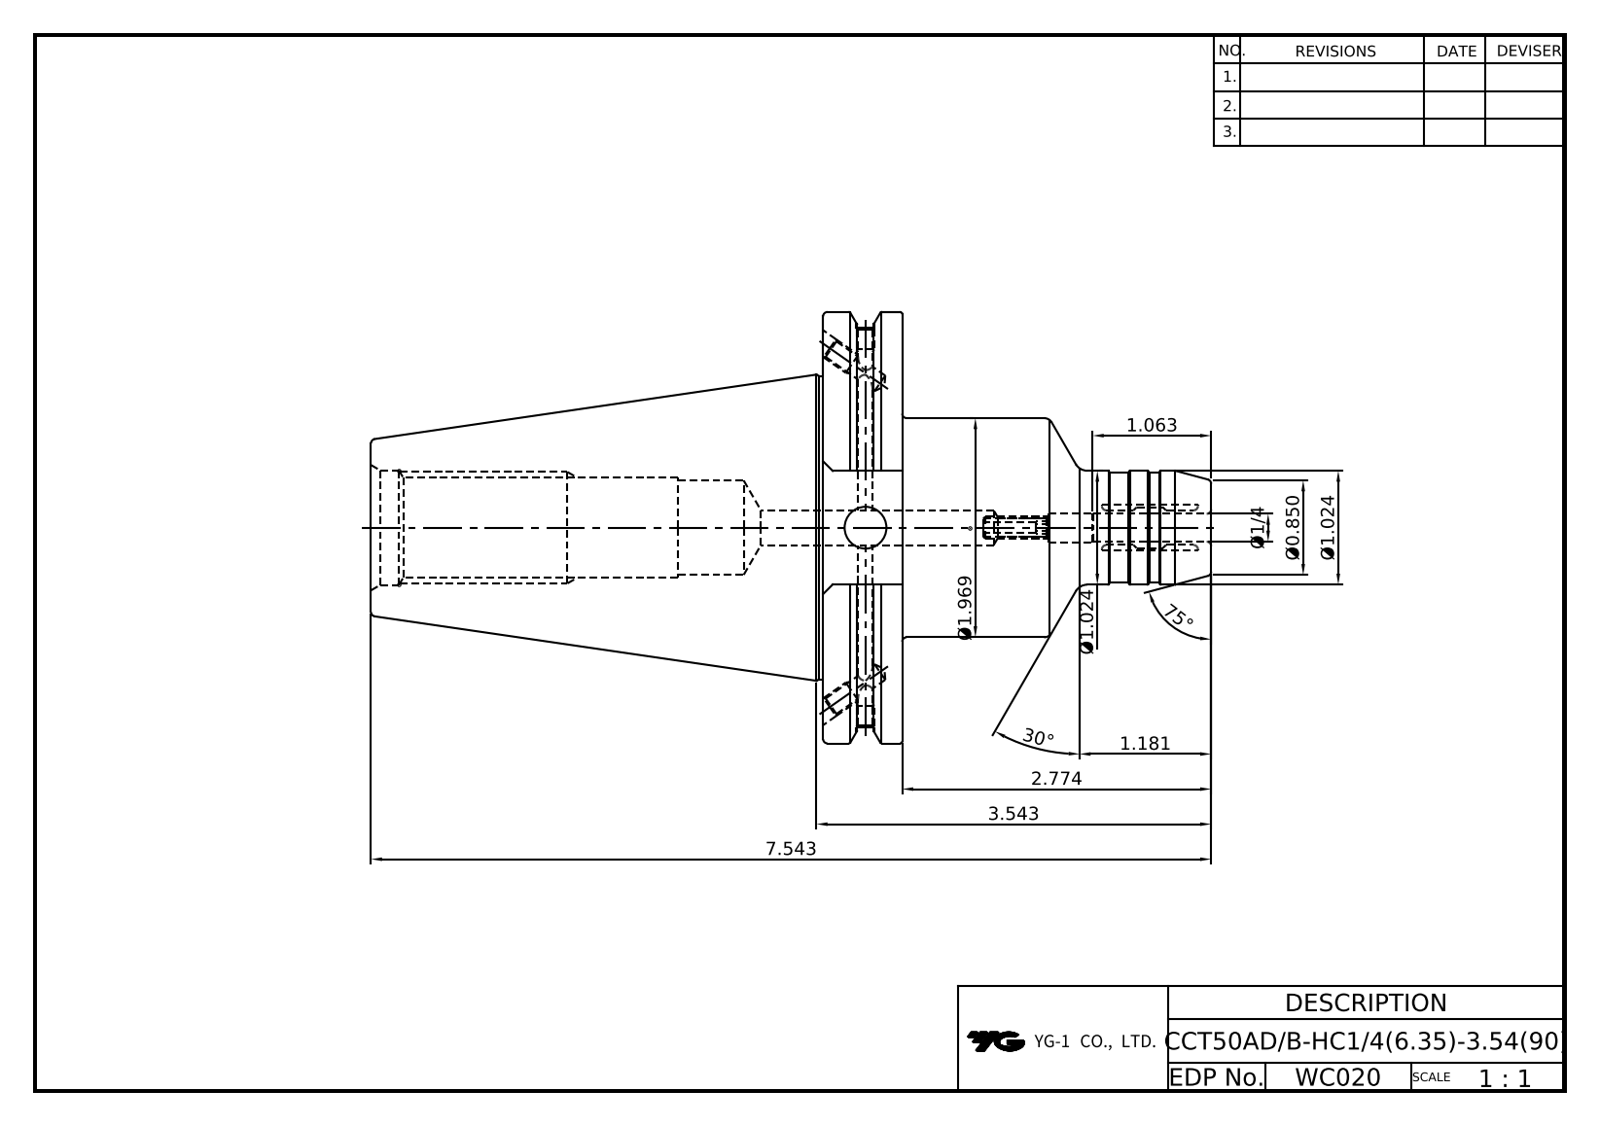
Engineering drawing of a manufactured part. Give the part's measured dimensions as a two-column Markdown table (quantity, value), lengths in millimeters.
| quantity | value |
| --- | --- |
| part name | CCT50ADB-HC6.35-90 |
| STEP written by | Autodesk Inventor 2022 (AUTOMOTIVE_DESIGN) |
| units | millimeters |
| bodies | 1 solid, 110 faces (38 planar, 33 cylindrical, 39 other) |
| overall size | 191.6 × 98.42 × 94.69 |
| volume | 421 825 mm³ |
| surface area | 53 408 mm² |
| round holes (diameter × count) | 3.24 × 2, 4.13 × 2, 4.2 × 2, 5 × 2, 4.3 × 1, 6.35 × 1, 6.8 × 1, 8 × 1, 9.53 × 1, 21.5 × 1, 21.97 × 1, 26.2 × 1 |
| round bosses / shafts (diameter × count) | 98.42 × 1, 91.29 × 1, 69.25 × 1, 50 × 1, 26 × 1, 25 × 1 |
| main face-to-face distances | 17.55, 103.1, 120.65, 73.03, 25.9, 191.6, 88.5, 70.95, 103.5, 0.4 |
